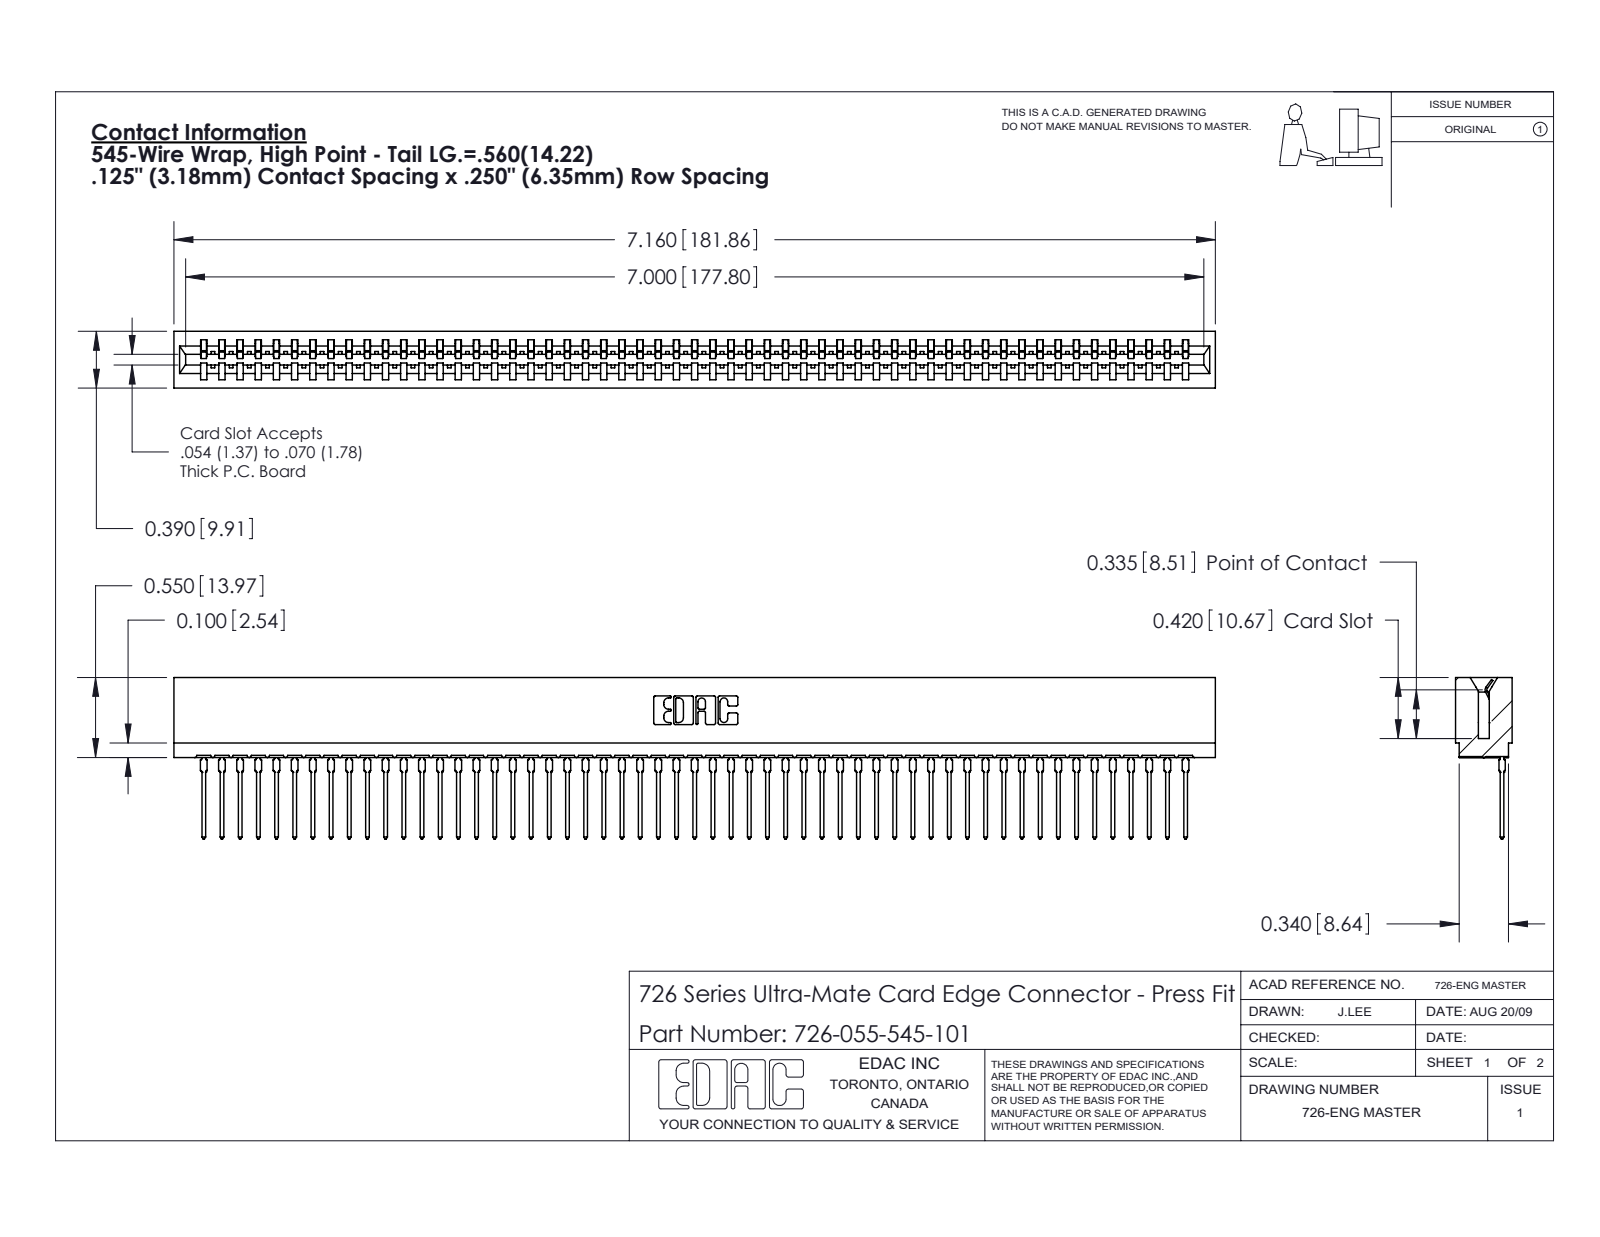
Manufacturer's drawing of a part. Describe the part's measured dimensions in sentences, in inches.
The part is named "746-292-001_545; 726-055-545-101; 726 Part_.515 Slot Depth - 01". Its 3-D file was written by "SolidWorks 2020 (CONFIG_CONTROL_DESIGN)". It is 56 solids with 6037 faces: 3520 planar, 1087 cylindrical and 1430 other. Overall it measures 7.16 by 1.109 by 0.39 inches. Its volume is 0.996 cubic inches and its surface area 40.09 square inches. Partial cylindrical surfaces (rounded edges, fillets, slot ends): 110 of radius 0.021, 56 of radius 0.015, 22 of radius 0.01, 6 of radius 0.007, 6 of radius 0.031, 4 of radius 0.005, 4 of radius 0.011, 3 of radius 0.026. The main face-to-face distances are 0.057, 0.333, 0.39, 0.025, 0.307, 0.25, 0.083, 0.275, 0.365, 0.032.
